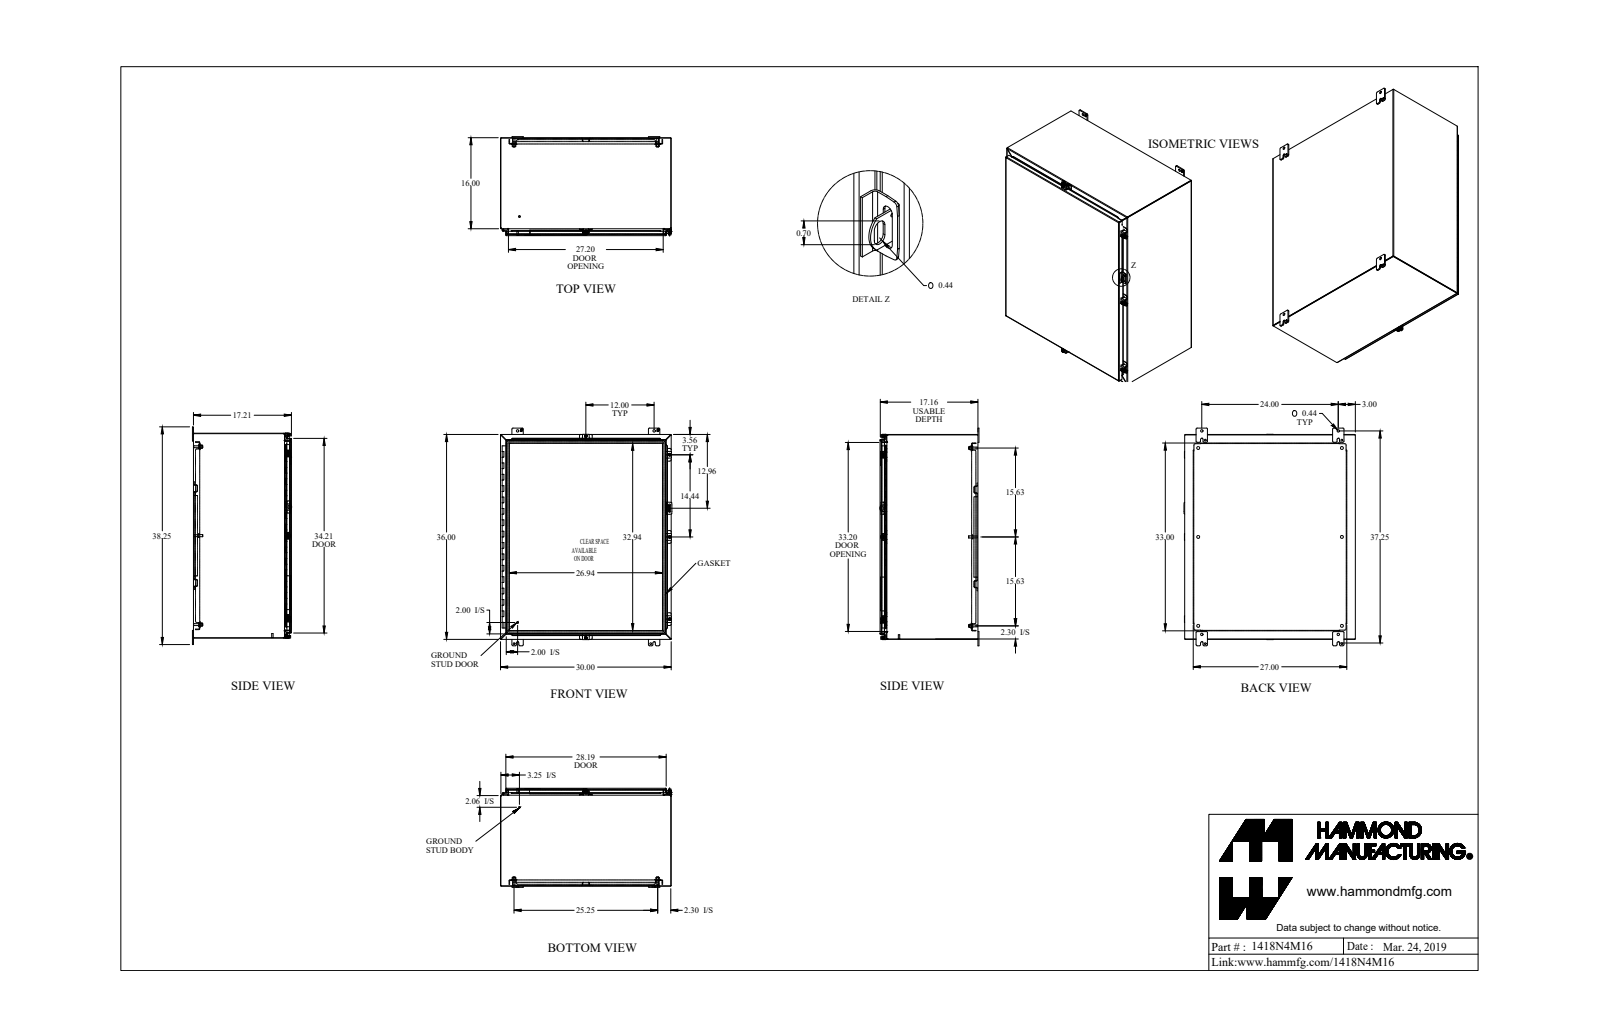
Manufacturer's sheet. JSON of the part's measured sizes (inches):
{"part_name": "1418N4M16_Default", "step_written_by": "SolidWorks 2019 (CONFIG_CONTROL_DESIGN)", "units": "inches", "bodies": {"solids": 54, "faces": 1823, "planar": 1063, "cylindrical": 650, "other": 110}, "overall_size": [38.25, 30.126, 17.437], "volume_in3": 457.3, "surface_area_in2": 12069, "round_holes": [[0.5, 6], [0.213, 5], [0.265, 5], [0.307, 4], [0.313, 4], [0.375, 4], [0.437, 4], [0.445, 2], [0.445, 2], [0.125, 1], [0.187, 1], [0.375, 1]], "round_bosses_or_shafts": [[0.65, 6], [0.375, 6], [0.33, 6], [0.5, 5], [0.39, 5], [0.244, 5], [1, 4], [0.281, 2]], "partial_cylinders_radius": [[0.188, 38], [0.25, 36], [0.048, 27], [0.143, 27], [0.036, 22], [0.108, 22], [0.116, 12], [0.125, 12]], "face_to_face_distances": [0.072, 0.072, 29.928, 17.066, 17.138, 17.138, 17.21, 35.928, 16.106, 16.034], "hole_center_spacings": [25.25, 40.176, 12.802, 12.803, 15.625, 15.625, 21.782, 24]}
